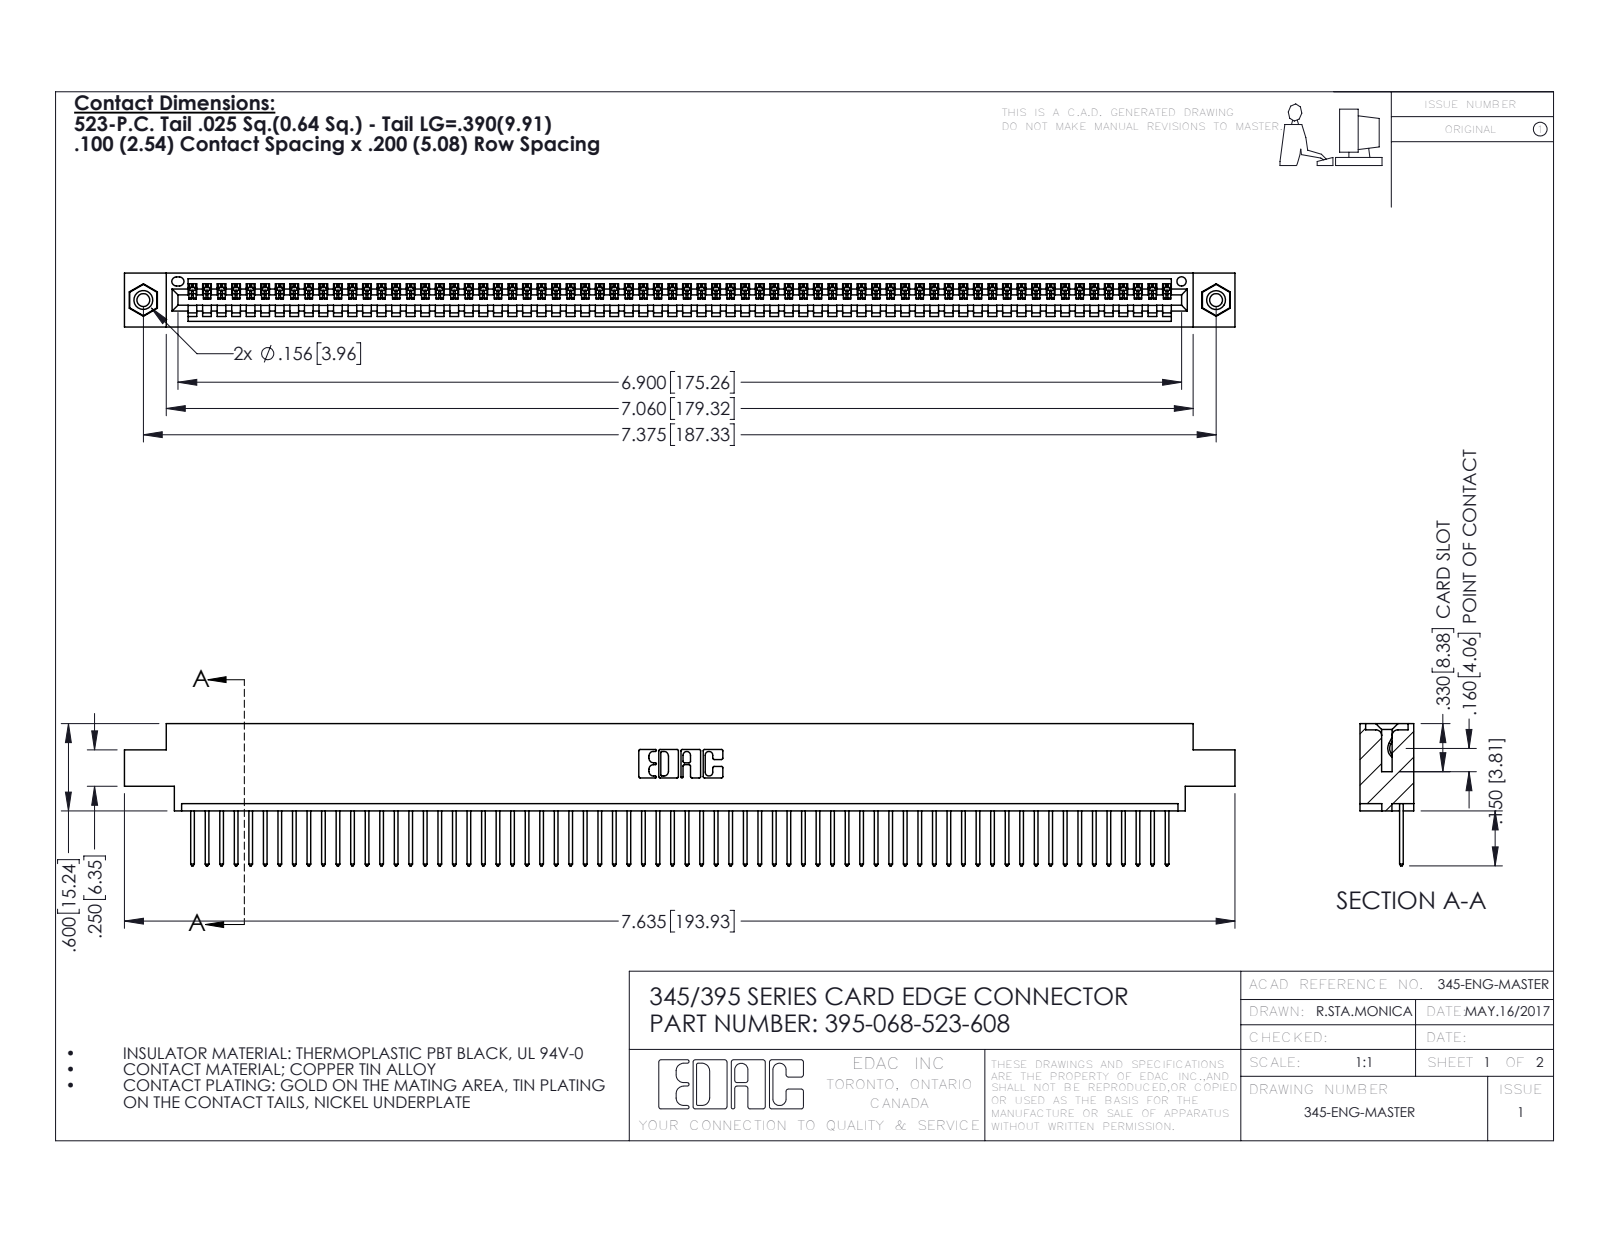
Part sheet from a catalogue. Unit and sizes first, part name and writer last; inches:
Units: inches
Overall size (bounding box): 7.635 × 0.977 × 0.37
Round holes (diameter × count): ⌀0.089 ×2, ⌀0.125 ×2, ⌀0.156 ×2, ⌀0.064 ×1
Round bosses / shafts (diameter × count): ⌀0.155 ×2
Partial cylindrical surfaces — rounded edges, fillets, slot ends (radius × count): R0.006 ×136, R0.01 ×136, R0.01 ×22, R0.007 ×6, R0.031 ×6, R0.026 ×3, R0.031 ×2, R0.04 ×2
Main face-to-face distances: 0.072, 0.298, 0.37, 0.098, 0.272, 0.025, 0.2, 0.225, 0.175, 0.149
Hole centre spacings: 0.27, 7.139, 7.375
Volume: 1.128 in³ · Surface area: 38.97 in²
Bodies: 71 solids, 4134 faces (2836 planar, 1282 cylindrical, 16 other)
Part name (STEP PRODUCT): 345-292-001_345-293-123; 345-250-001_345-250-003-102; 345 Part_0.170 Offset - 0.156 Dia-TI; 395-068-523-608
STEP written by: SolidWorks 2016 (CONFIG_CONTROL_DESIGN)
